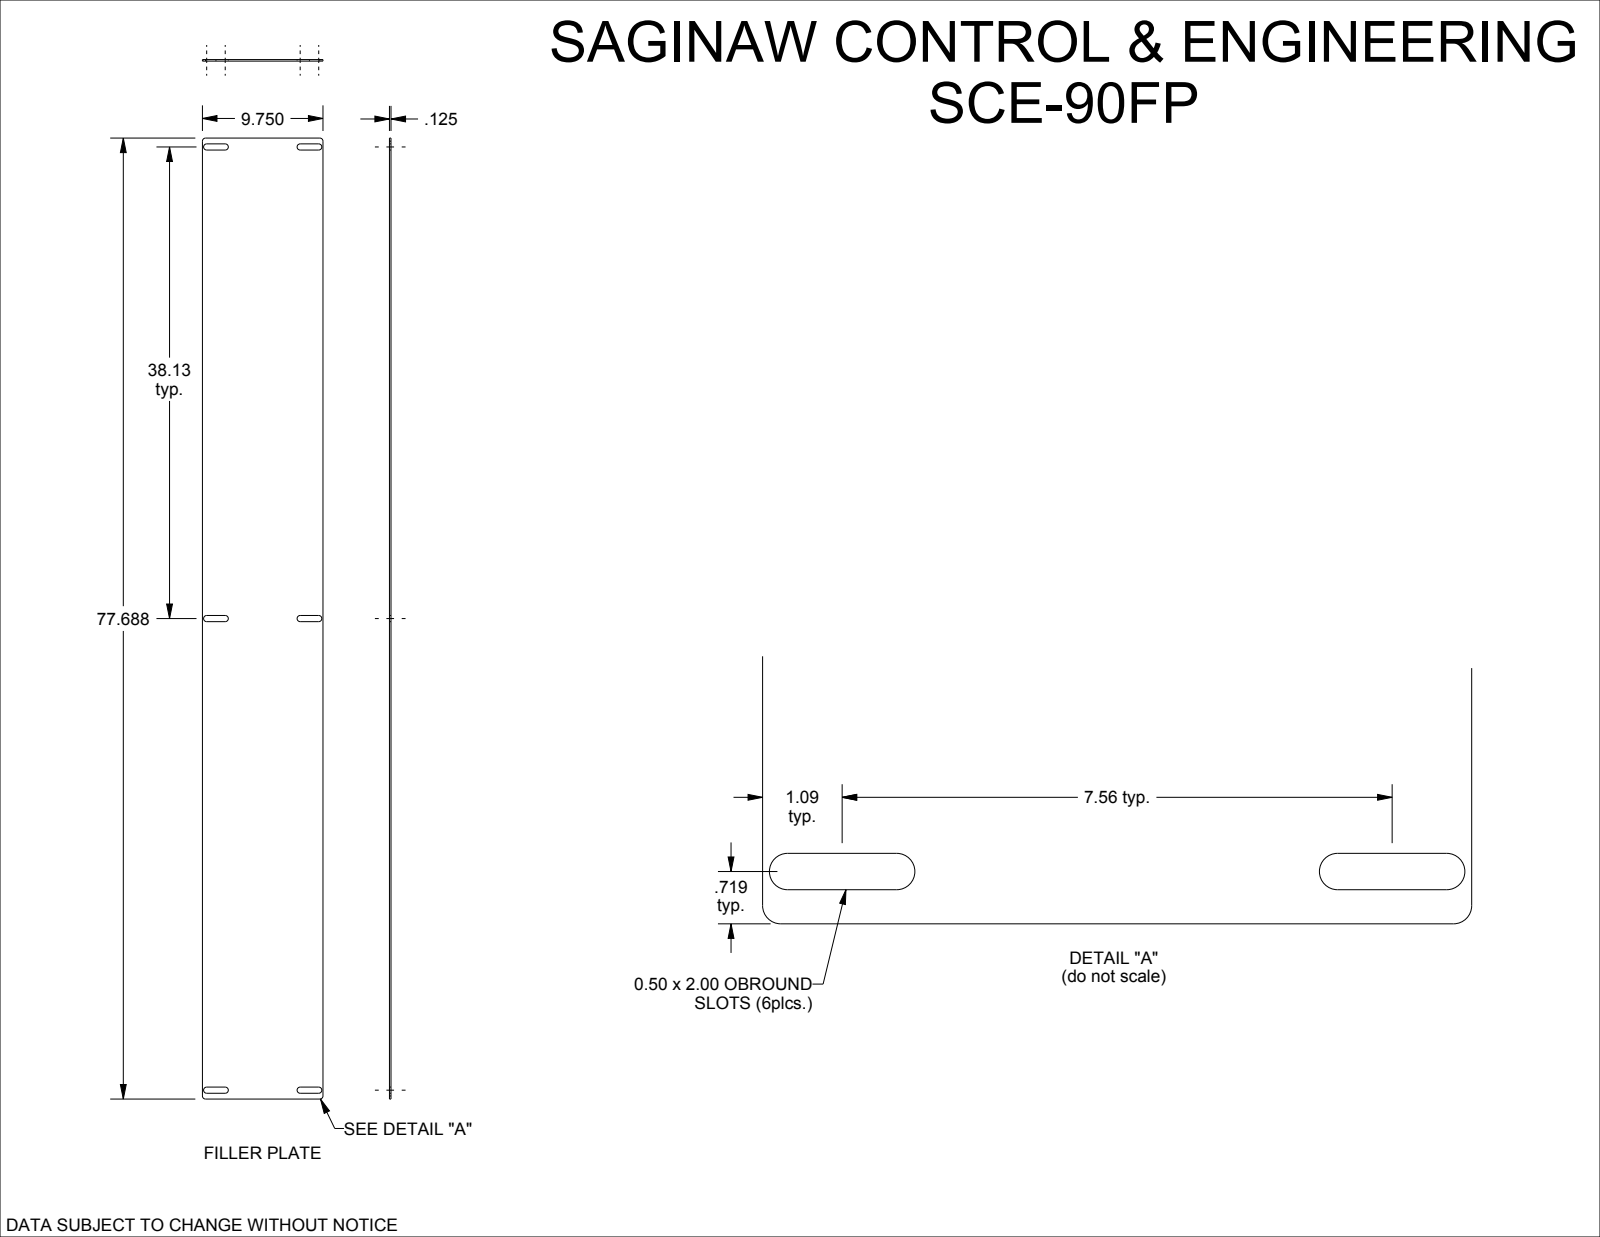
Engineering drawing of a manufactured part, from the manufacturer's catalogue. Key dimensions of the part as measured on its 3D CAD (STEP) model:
Part name (STEP PRODUCT): SCE-90FP
STEP written by: SolidWorks 2023 (AUTOMOTIVE_DESIGN)
Units: inches
Bodies: 1 solid, 46 faces (30 planar, 16 cylindrical, 0 other)
Overall size (bounding box): 77.688 × 9.75 × 0.125
Volume: 93.97 in³ · Surface area: 1 529 in²
Partial cylindrical surfaces — rounded edges, fillets, slot ends (radius × count): R0.25 ×16
Main face-to-face distances: 0.125, 9.75, 38.125, 77.687, 0.5, 38.594, 39.094, 0.969, 76.719, 0.469
